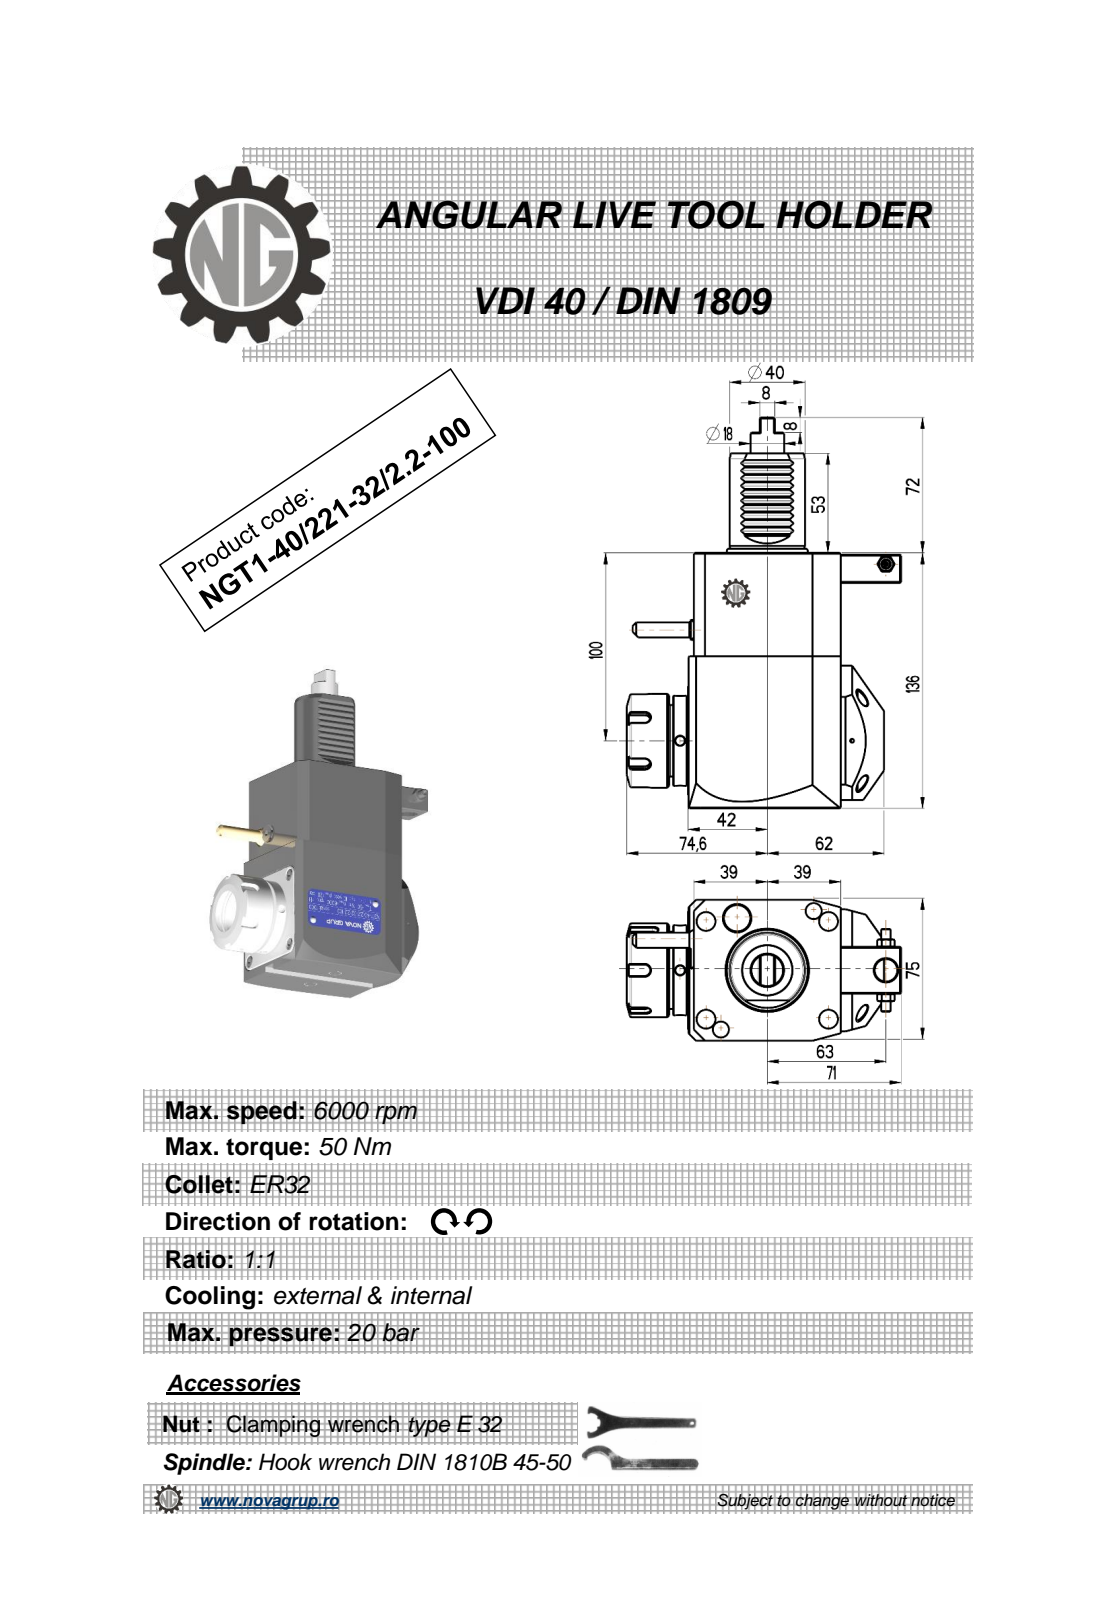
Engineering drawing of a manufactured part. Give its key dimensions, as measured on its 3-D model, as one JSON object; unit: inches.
{"part_name": "NGT1_40_221_32__2_100", "step_written_by": "PRO/ENGINEER BY PARAMETRIC TECHNOLOGY CORPORATION, 2010280 (CONFIG_CONTROL_DESIGN)", "units": "inches", "bodies": {"solids": 1, "faces": 405, "planar": 189, "cylindrical": 89, "other": 127}, "overall_size": [8.189, 5.732, 3.016], "volume_in3": 60.91, "surface_area_in2": 118.1, "round_holes": [[0.197, 3], [0.118, 1], [0.165, 1], [0.374, 1], [0.472, 1], [1.063, 1]], "round_bosses_or_shafts": [[1.969, 1], [1.89, 1], [1.614, 1], [1.575, 1], [0.701, 1], [0.441, 1], [0.353, 1], [0.315, 1]], "partial_cylinders_radius": [[0.01, 12], [0.012, 10], [0.009, 6], [0.118, 5], [0.031, 2], [0.02, 1], [1.575, 1]], "face_to_face_distances": [2.953, 5.354, 3.071, 3.189, 0.118, 0.11, 3.181, 2.126, 0.984, 0.295], "hole_center_spacings": [1.461, 2.407, 3.642, 4.301, 5.674]}
